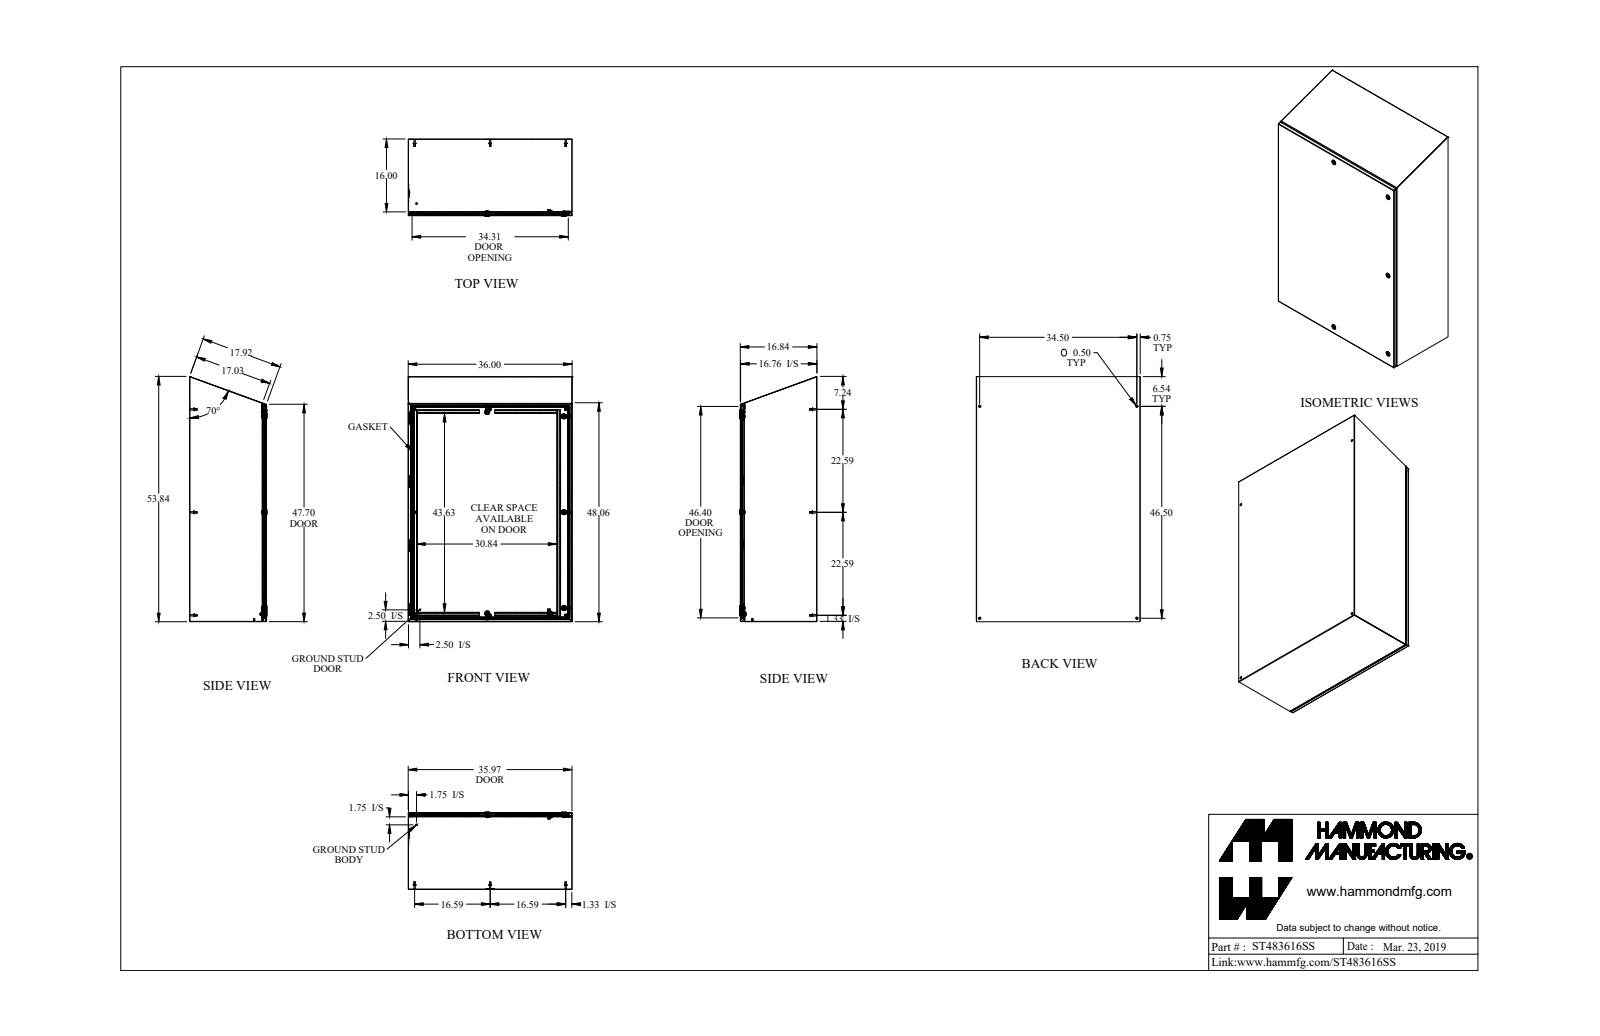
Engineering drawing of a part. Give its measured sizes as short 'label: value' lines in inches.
name: ST483616SS
written by: SolidWorks 2018 (AUTOMOTIVE_DESIGN)
unit: in
bodies: 67 solids, 1731 faces (915 planar, 552 cylindrical, 264 other)
size: 53.791 × 36 × 16.997
volume: 520.3 in³; area: 14 640 in²
holes: 9× ⌀0.5, 5× ⌀0.197, 5× ⌀0.387, 5× ⌀0.63, 5× ⌀0.768, 1× ⌀0.172, 1× ⌀0.196, 1× ⌀0.24, 1× ⌀0.242, 1× ⌀0.275, 1× ⌀0.375
bosses: 11× ⌀0.625, 10× ⌀0.313, 8× ⌀0.275, 5× ⌀1.1, 5× ⌀0.236, 3× ⌀0.785, 3× ⌀0.625, 3× ⌀0.525
rounds: 24× R0.01, 24× R0.048, 19× R0.036, 18× R0.108, 17× R0.062, 12× R0.125, 10× R0.094, 9× R0.016
face distances: 0.072, 16.765, 16.693, 16.837, 35.928, 35.856, 36, 15.928, 0.837, 0.038
hole spacings: 21.03, 34.5, 46.5, 57.901, 2.44, 2.494, 3.543, 4.444
